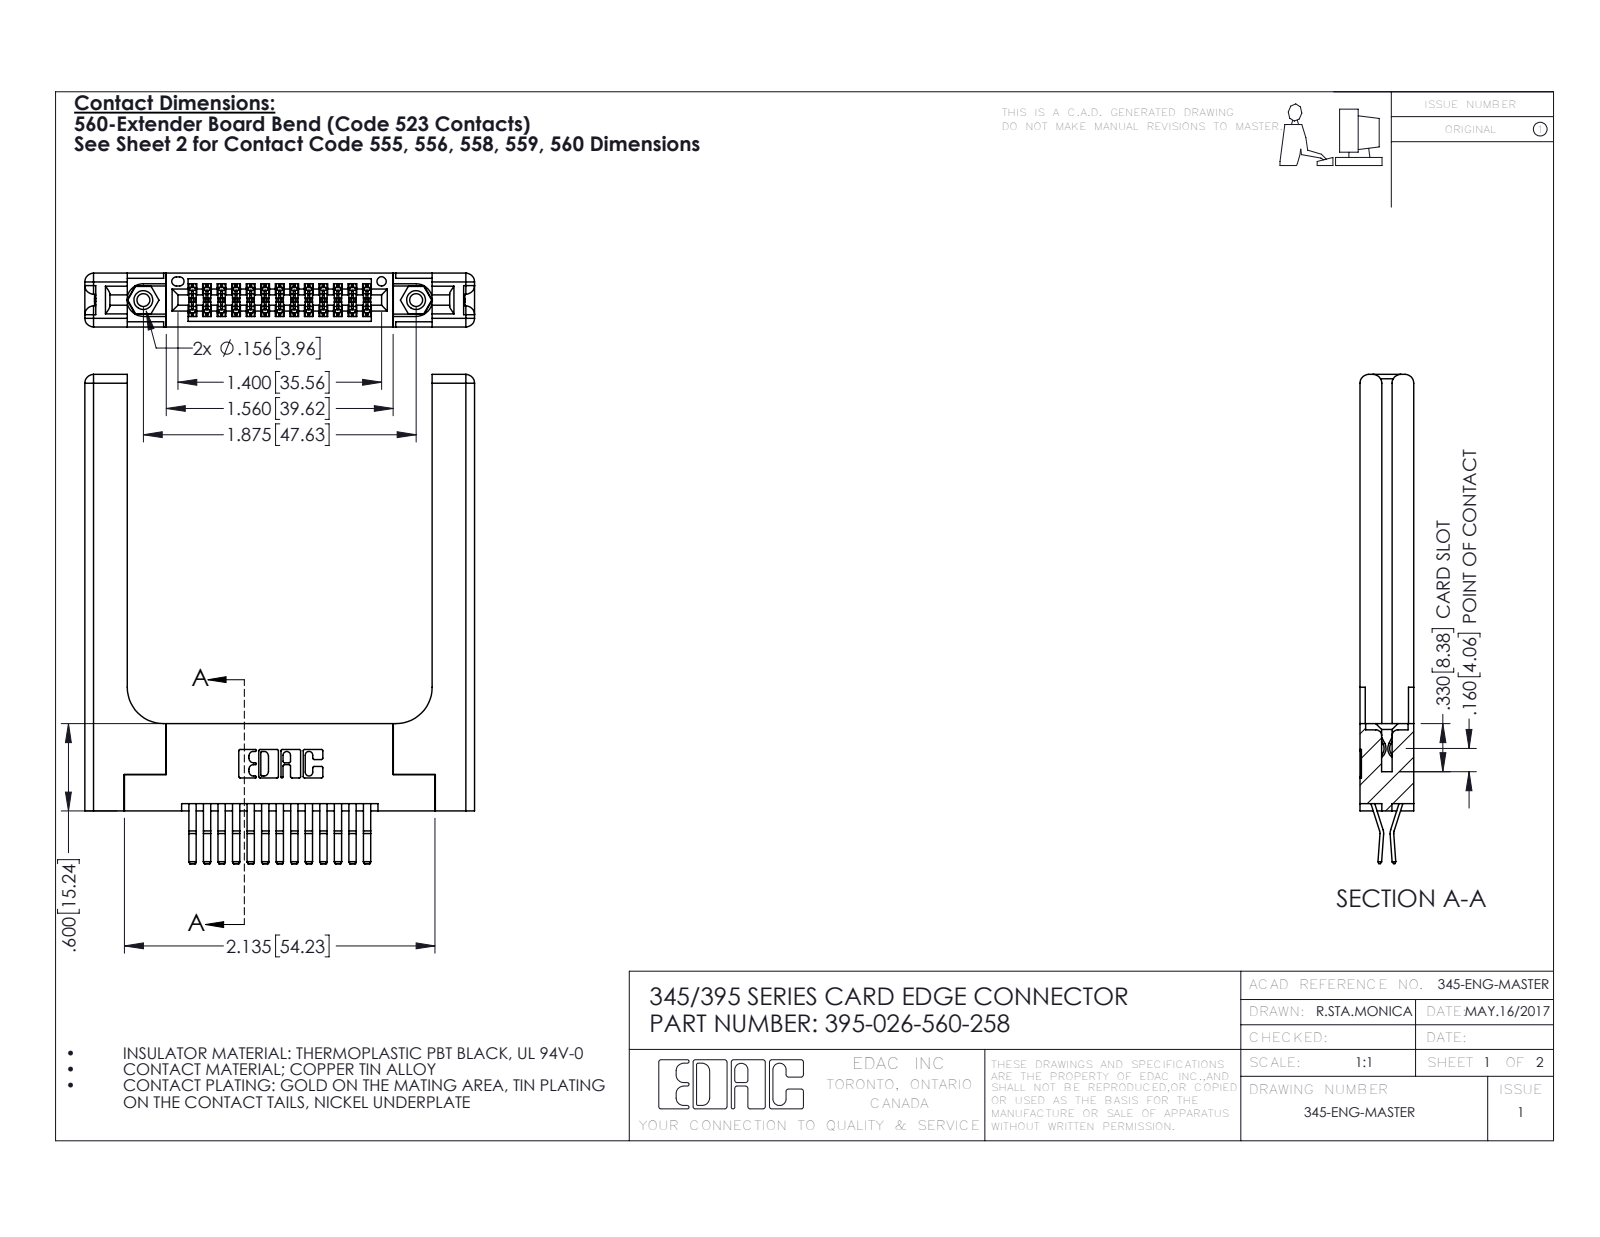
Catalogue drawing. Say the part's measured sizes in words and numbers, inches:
The part is named "345-250-001_345-250-001-102; 395-026-560-258; 345 Part_Flush Mounting Lugs - 0.156 Dia-TH; 345-220-058_345-220-058 (+1 more)". Its 3-D file was written by "SolidWorks 2016 (CONFIG_CONTROL_DESIGN)". It is 31 solids with 1734 faces: 1086 planar, 588 cylindrical and 60 other. Overall it measures 3.362 by 2.679 by 0.37 inches. Its volume is 0.915 cubic inches and its surface area 22.57 square inches. Round holes: 2 of diameter 0.089, 2 of diameter 0.125, 2 of diameter 0.156, 1 of diameter 0.064. Round bosses or shafts: 2 of diameter 0.155. Partial cylindrical surfaces (rounded edges, fillets, slot ends): 39 of radius 0.006, 22 of radius 0.01, 16 of radius 0.06, 6 of radius 0.007, 6 of radius 0.031, 3 of radius 0.026, 2 of radius 0.01, 2 of radius 0.014. The main face-to-face distances are 0.37, 0.072, 0.298, 0.077, 0.148, 0.15, 0.025, 0.22, 0.2, 0.225. The hole center spacings are 0.27, 1.643, 1.875.
